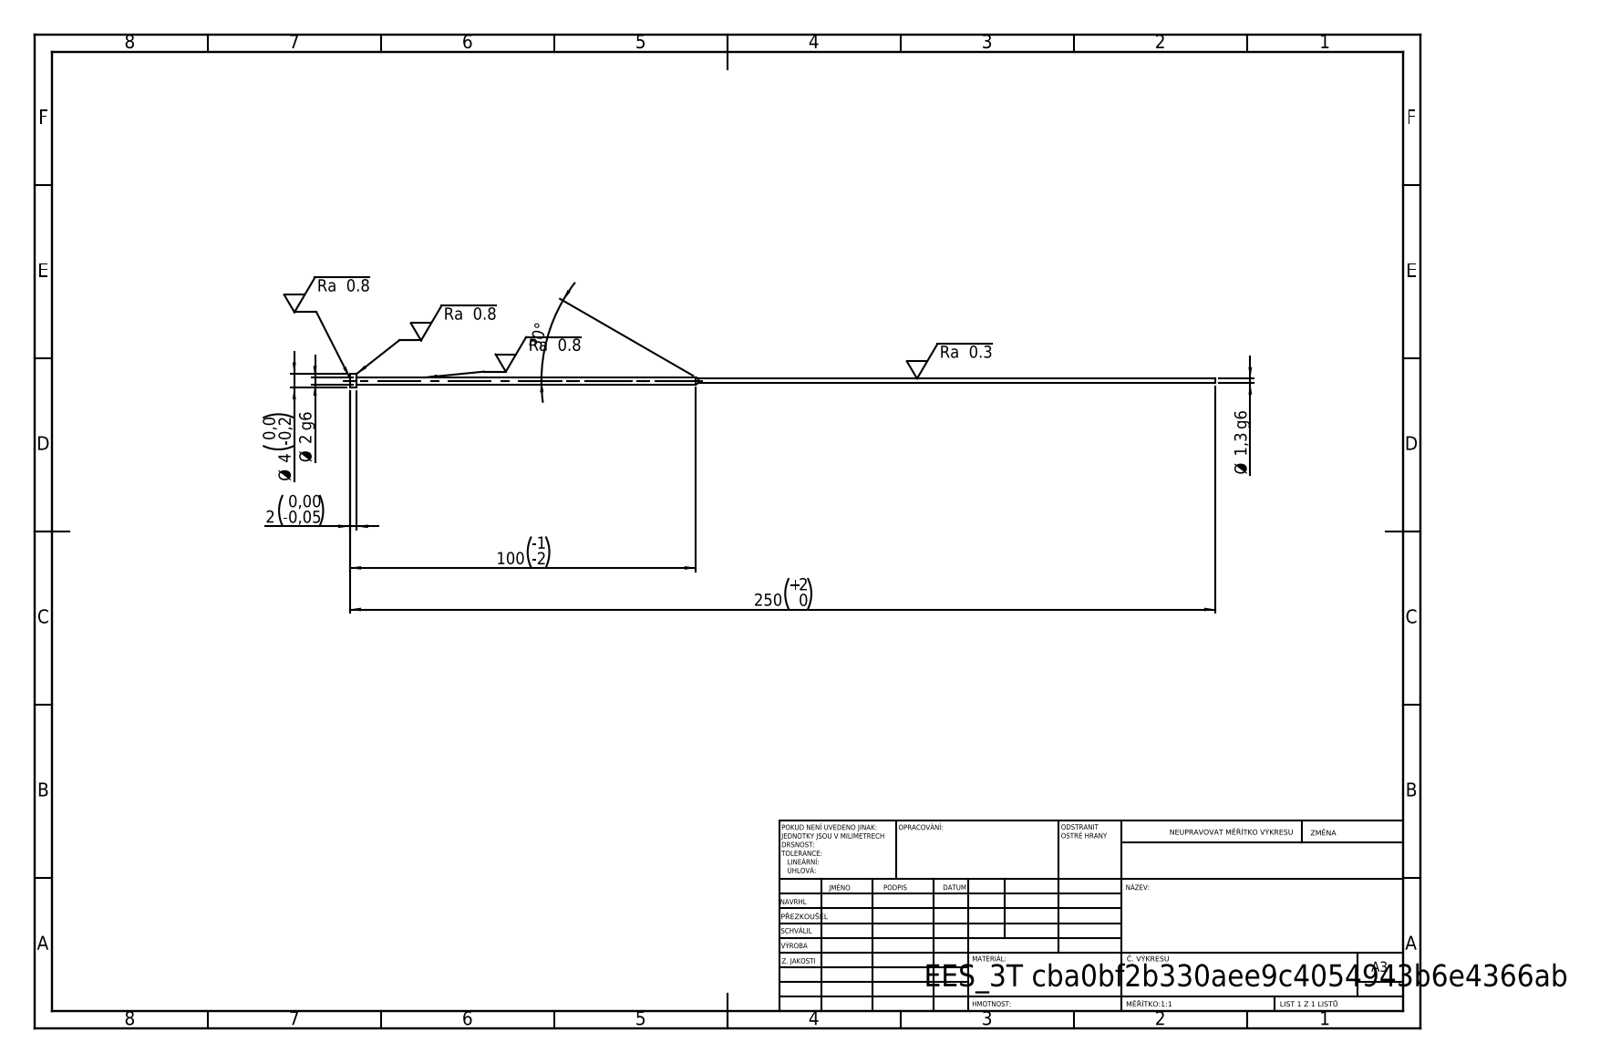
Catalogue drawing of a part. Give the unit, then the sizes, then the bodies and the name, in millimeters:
Units: millimetres
Overall size (bounding box): 250 × 4 × 4
Round bosses / shafts (diameter × count): ⌀4 ×1, ⌀2 ×1, ⌀1.3 ×1
Main face-to-face distances: 2, 248, 250
Volume: 533 mm³ · Surface area: 1 278 mm²
Bodies: 1 solid, 11 faces (3 planar, 6 cylindrical, 2 other)
STEP written by: SolidWorks 2019 (CONFIG_CONTROL_DESIGN)
